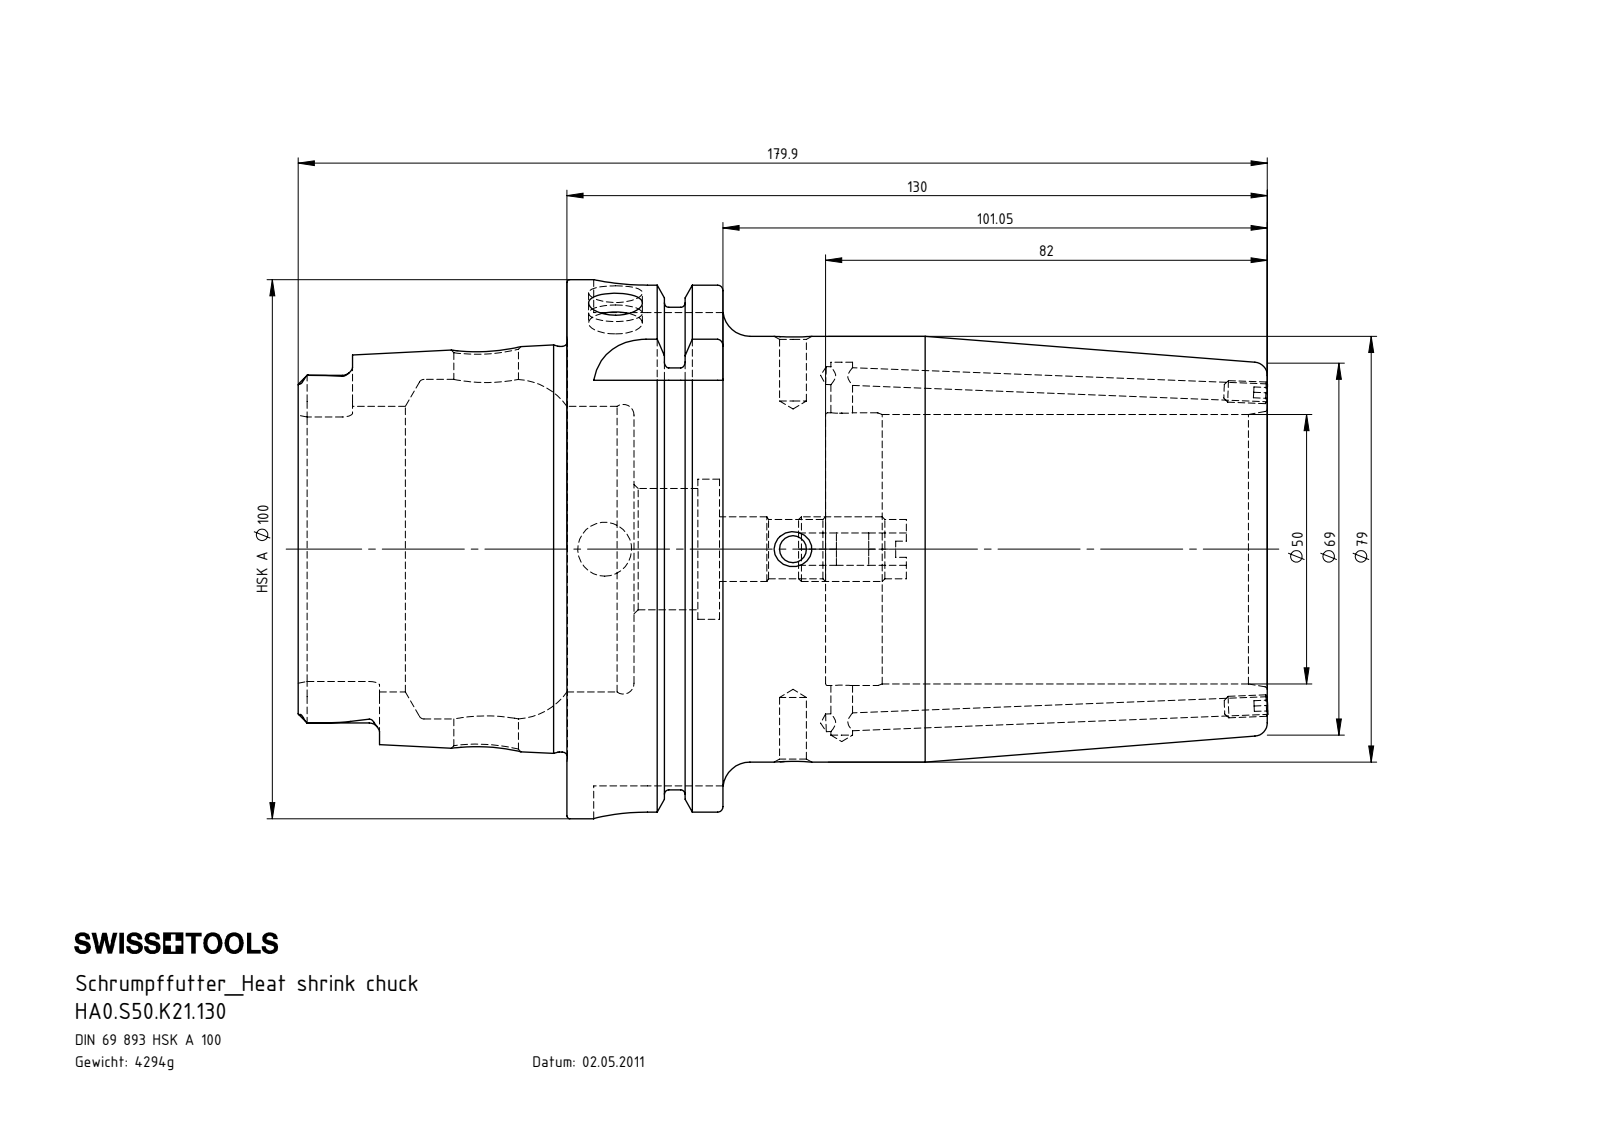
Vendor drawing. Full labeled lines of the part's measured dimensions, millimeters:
Part name (STEP PRODUCT): HA0-S50.K21.130; ERU-CJ3.001.008; ERU-AN5.K01.020_A; HA0-S50.K21.130_C_Fertigbearbeitung
STEP written by: SolidWorks 2012 (CONFIG_CONTROL_DESIGN)
Units: millimetres
Bodies: 4 solids, 296 faces (97 planar, 86 cylindrical, 113 other)
Overall size (bounding box): 180 × 100 × 100
Volume: 547 004 mm³ · Surface area: 89 580 mm²
Round holes (diameter × count): ⌀10 ×3, ⌀3.3 ×2, ⌀5 ×2, ⌀12 ×2, ⌀4 ×1, ⌀6 ×1, ⌀11 ×1, ⌀22.5 ×1, ⌀26 ×1, ⌀50 ×1, ⌀50.6 ×1, ⌀53 ×1
Round bosses / shafts (diameter × count): ⌀4 ×2, ⌀100 ×1, ⌀91.95 ×1, ⌀79 ×1, ⌀75.26 ×1
Partial cylindrical surfaces — rounded edges, fillets, slot ends (radius × count): R1.9 ×6, R4.88 ×4, R10 ×4
Main face-to-face distances: 48, 12.45, 35.55, 28.95, 16.5, 19.05, 130, 117.55, 101.05, 82
Hole centre spacings: 9.05, 34.95, 56.95, 66
